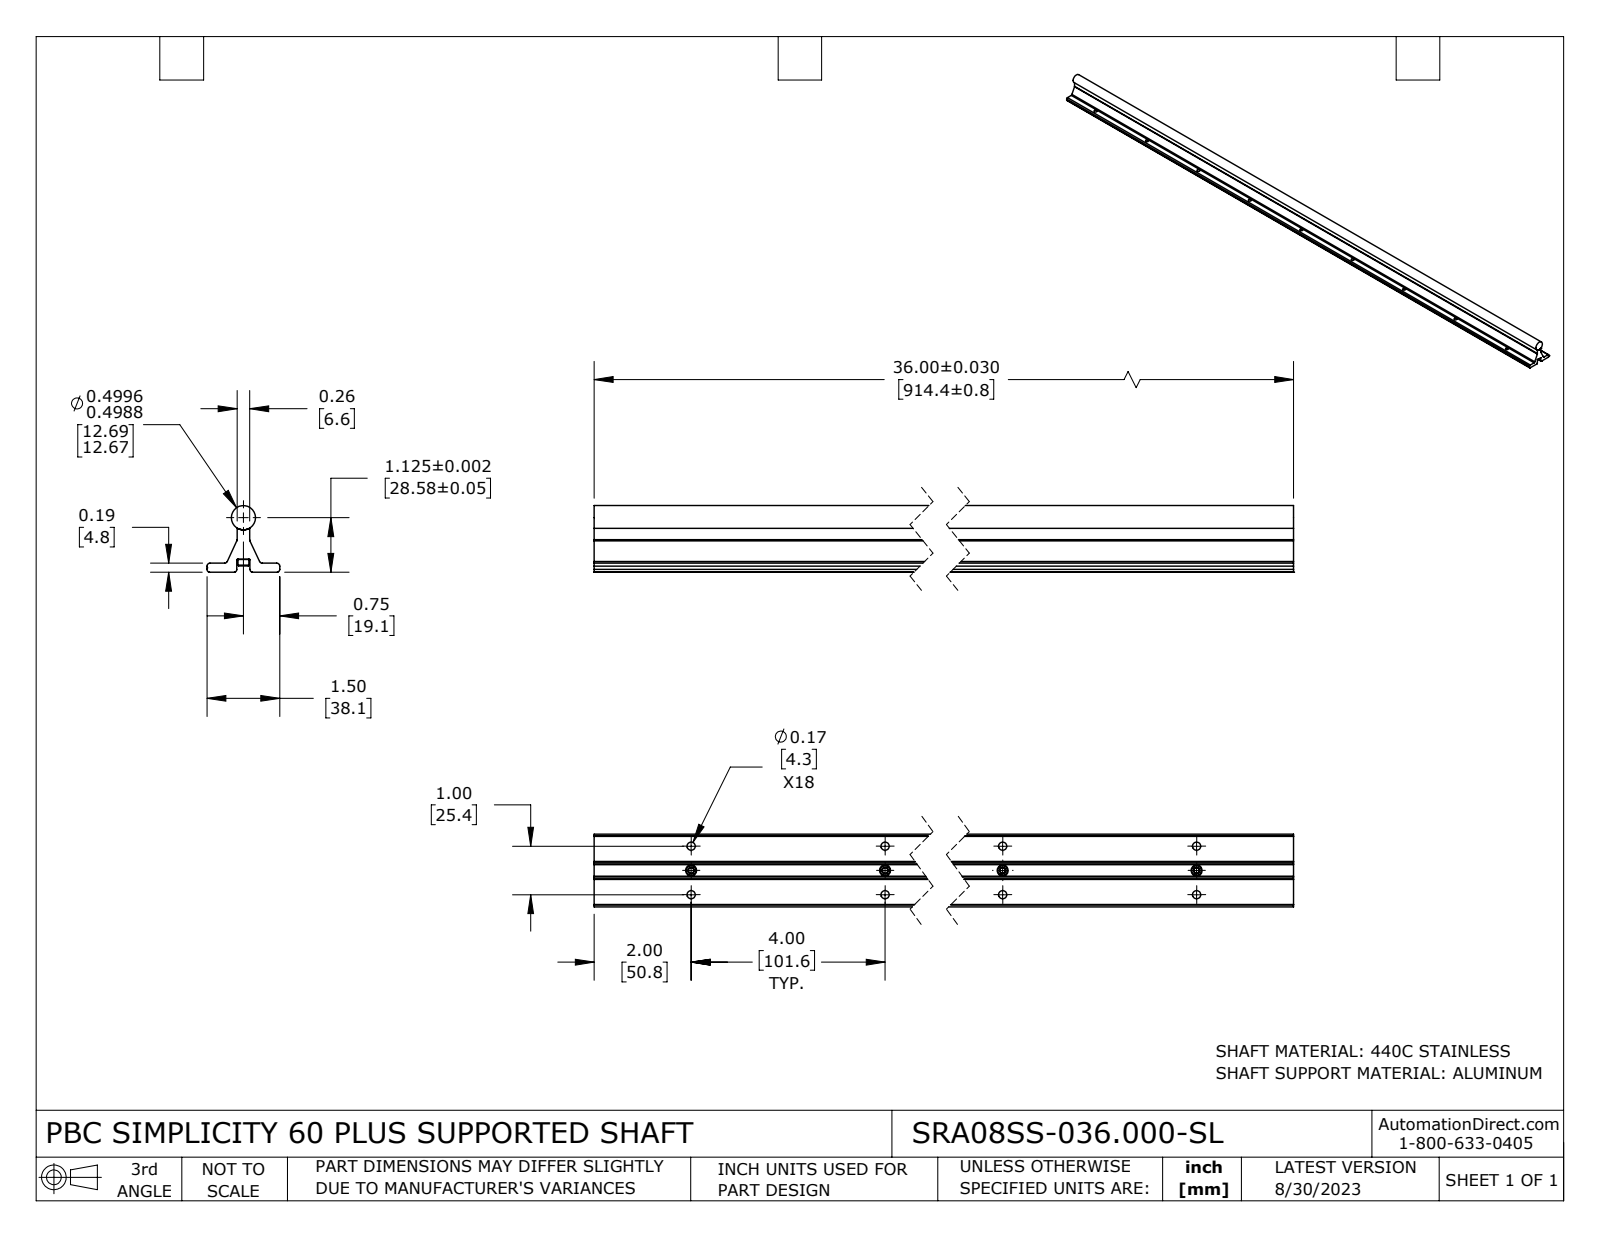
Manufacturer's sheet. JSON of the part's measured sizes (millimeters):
{"part_name": "SRA08SS-036.000-SL", "step_written_by": "SolidWorks 2021 (CONFIG_CONTROL_DESIGN)", "units": "millimeters", "bodies": {"solids": 11, "faces": 401, "planar": 126, "cylindrical": 140, "other": 135}, "overall_size": [914.4, 38.1, 34.9], "volume_mm3": 402600, "surface_area_mm2": 156600, "round_holes": [[4.3, 27], [2.9, 9], [4, 9]], "round_bosses_or_shafts": [[5.7, 9], [3.5, 9], [12.7, 1]], "partial_cylinders_radius": [[1.5, 8], [0.4, 2], [1.6, 1], [1.6, 1]], "face_to_face_distances": [4.7, 6.9, 6.7, 2.1, 6.6, 15.6, 15.7, 22.4, 22.5, 38.1], "hole_center_spacings": [102.4, 203.6, 101.6, 305.1, 203.2, 406.6, 12.7, 304.8]}
